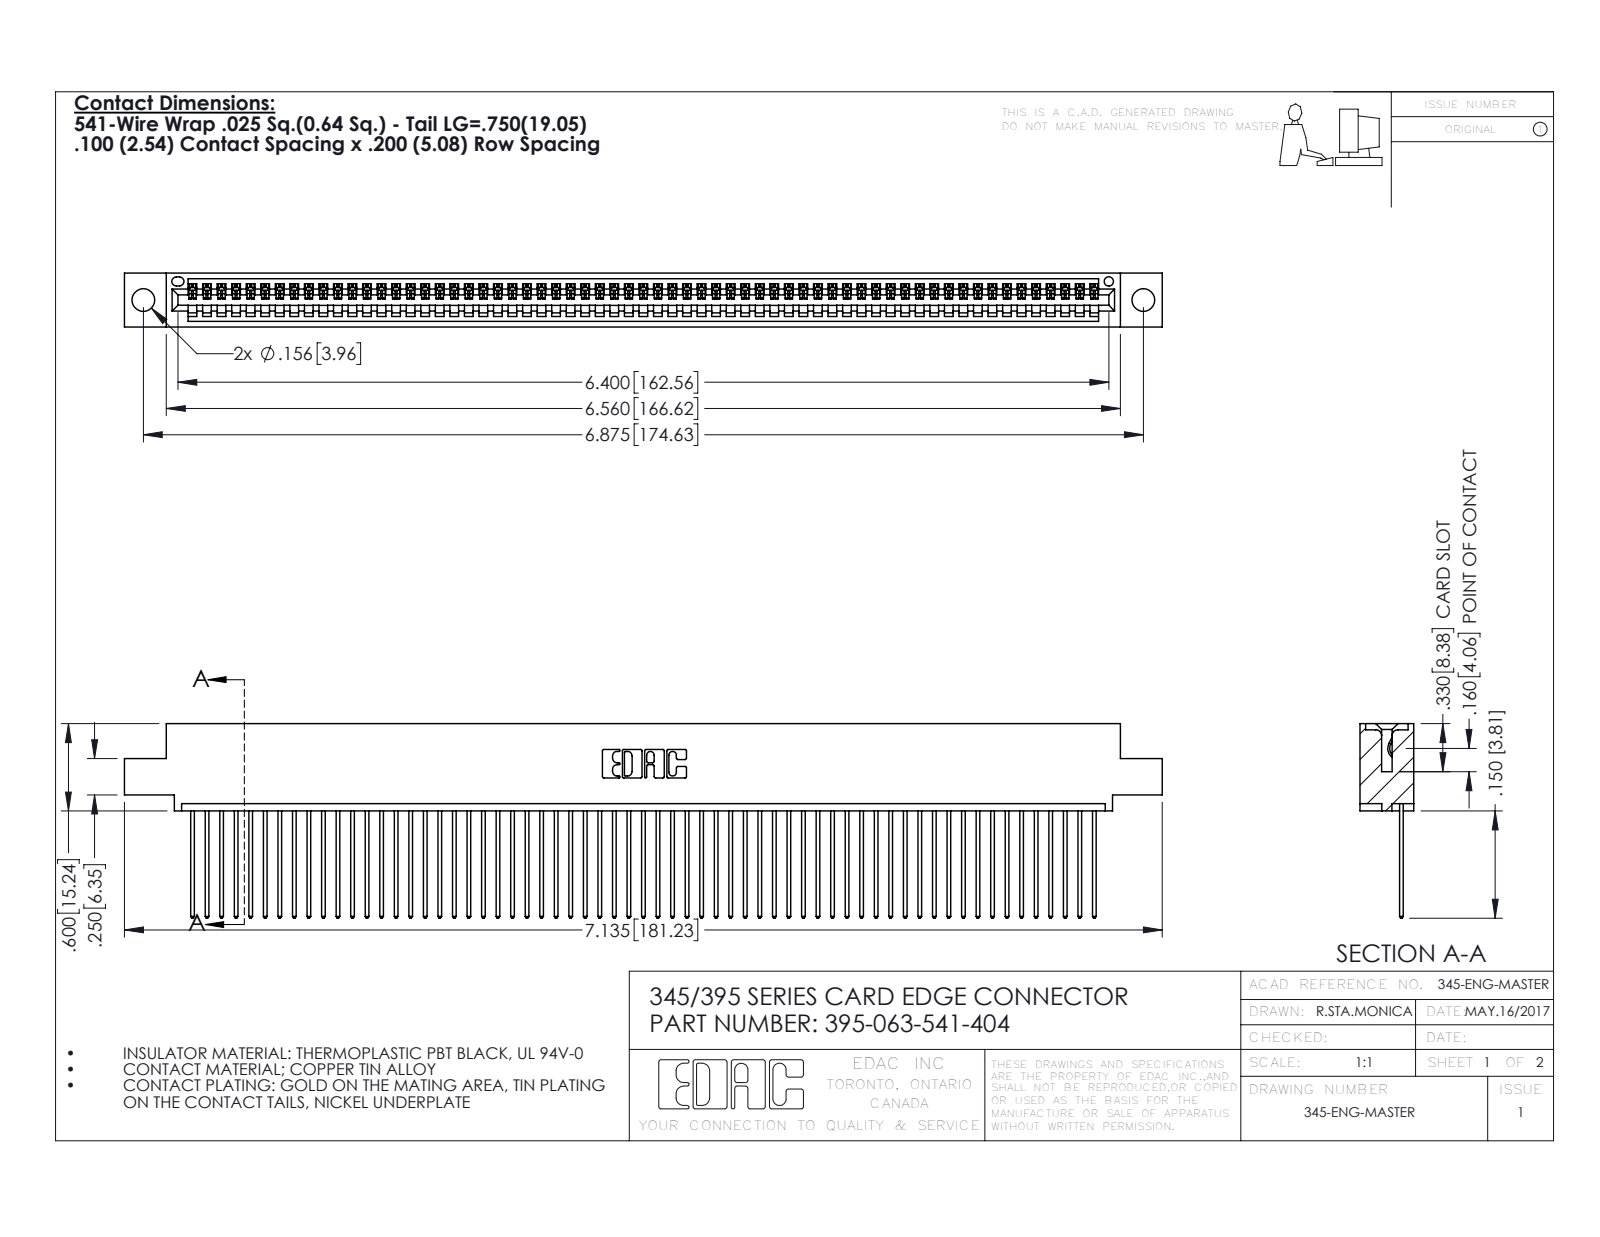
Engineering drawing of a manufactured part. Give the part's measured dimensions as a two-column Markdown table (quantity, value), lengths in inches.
| quantity | value |
| --- | --- |
| part name | 395-063-541-404; 345-292-001_345-293-141; 345 Part_0.110 Offset - 0.156 Dia-TH |
| STEP written by | SolidWorks 2016 (CONFIG_CONTROL_DESIGN) |
| units | inches |
| bodies | 64 solids, 3784 faces (2604 planar, 1180 cylindrical, 0 other) |
| overall size | 7.135 × 1.337 × 0.37 |
| volume | 1.064 in³ |
| surface area | 38.08 in² |
| round holes (diameter × count) | 0.156 × 2, 0.064 × 1 |
| partial cylindrical surfaces (radius × count) | 0.006 × 126, 0.01 × 126, 0.01 × 22, 0.007 × 6, 0.031 × 6, 0.026 × 3, 0.031 × 2, 0.04 × 2 |
| main face-to-face distances | 0.072, 0.298, 0.098, 0.272, 0.025, 0.37, 0.2, 0.225, 0.149, 0.072 |
| hole center spacings | 0.27, 6.639, 6.875 |
